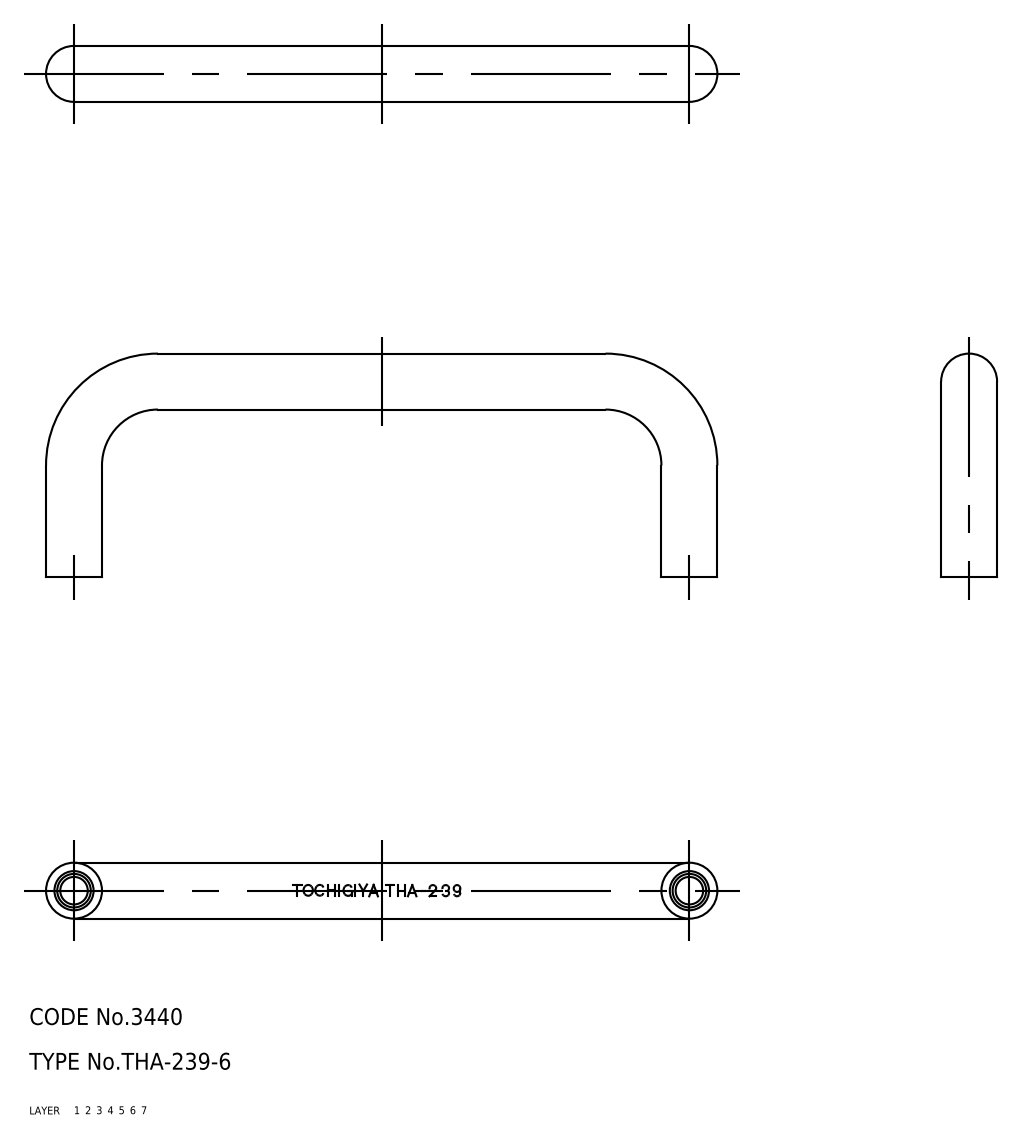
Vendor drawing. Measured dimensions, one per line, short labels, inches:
name: pull
written by: CADfix (AUTOMOTIVE_DESIGN)
unit: in
bodies: 1 solid, 18 faces (0 planar, 0 cylindrical, 18 other)
size: 4.724 × 1.575 × 0.394
volume: 0.779 in³; area: 8.851 in²
